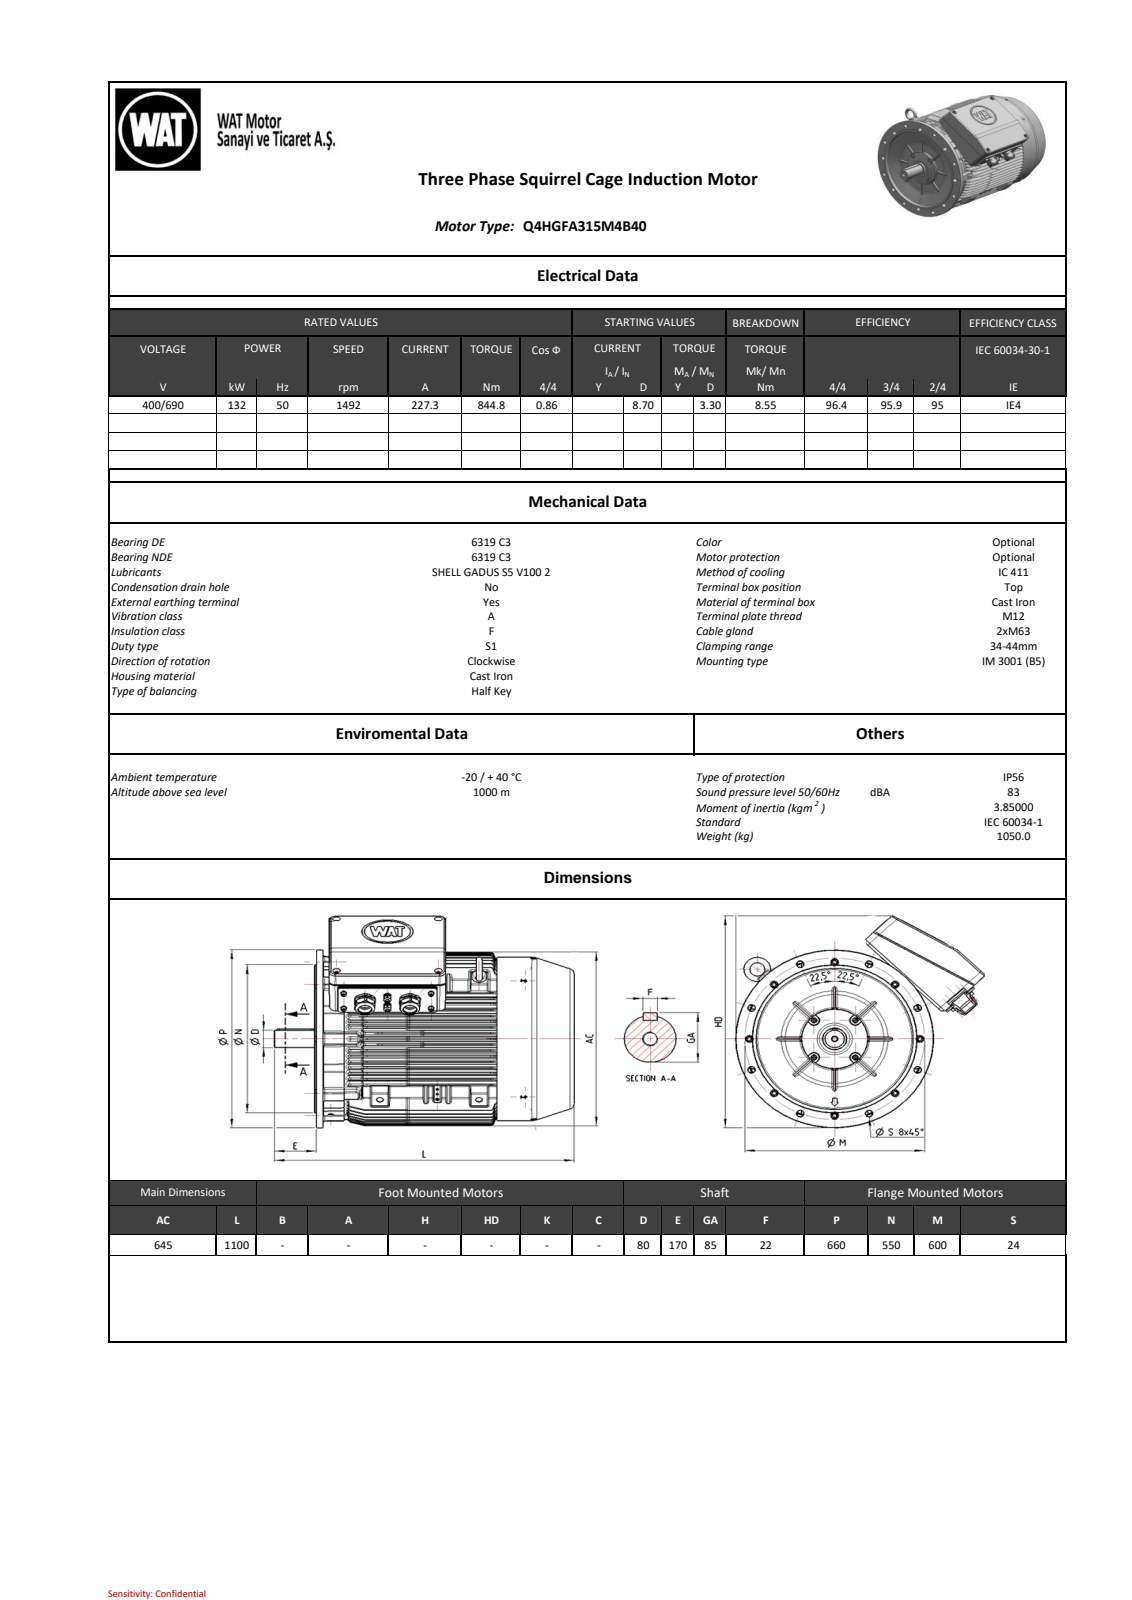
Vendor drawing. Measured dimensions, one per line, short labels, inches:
name: 26009910674F4pon
written by: SIEMENS PLM Software NX 11.0 (AUTOMOTIVE_DESIGN)
unit: in
bodies: 0 solids, 5868 faces (2692 planar, 1200 cylindrical, 1976 other)
size: 43.307 × 32.645 × 30.933
holes: 8× ⌀0.945, 8× ⌀1.024, 7× ⌀0.787, 5× ⌀0.335, 4× ⌀0.354, 4× ⌀0.866, 2× ⌀0.157, 2× ⌀0.315, 2× ⌀0.472, 2× ⌀0.476, 2× ⌀0.591, 2× ⌀0.827
bosses: 8× ⌀0.63, 7× ⌀0.787, 4× ⌀0.394, 2× ⌀2.551, 2× ⌀1.969, 1× ⌀25.984, 1× ⌀23.898, 1× ⌀22.244
rounds: 464× R0.236, 162× R0.118, 66× R0.082, 61× R0.103, 35× R0.031, 26× R0.394, 24× R0.059, 16× R0.016
face distances: 4.606, 0.815, 12.014, 1.634, 11.195, 0.819, 10.38, 9.546, 3.283, 10.372
hole spacings: 19.153, 3.113, 4.53, 4.531, 8.588, 11.811, 12.805, 12.806
